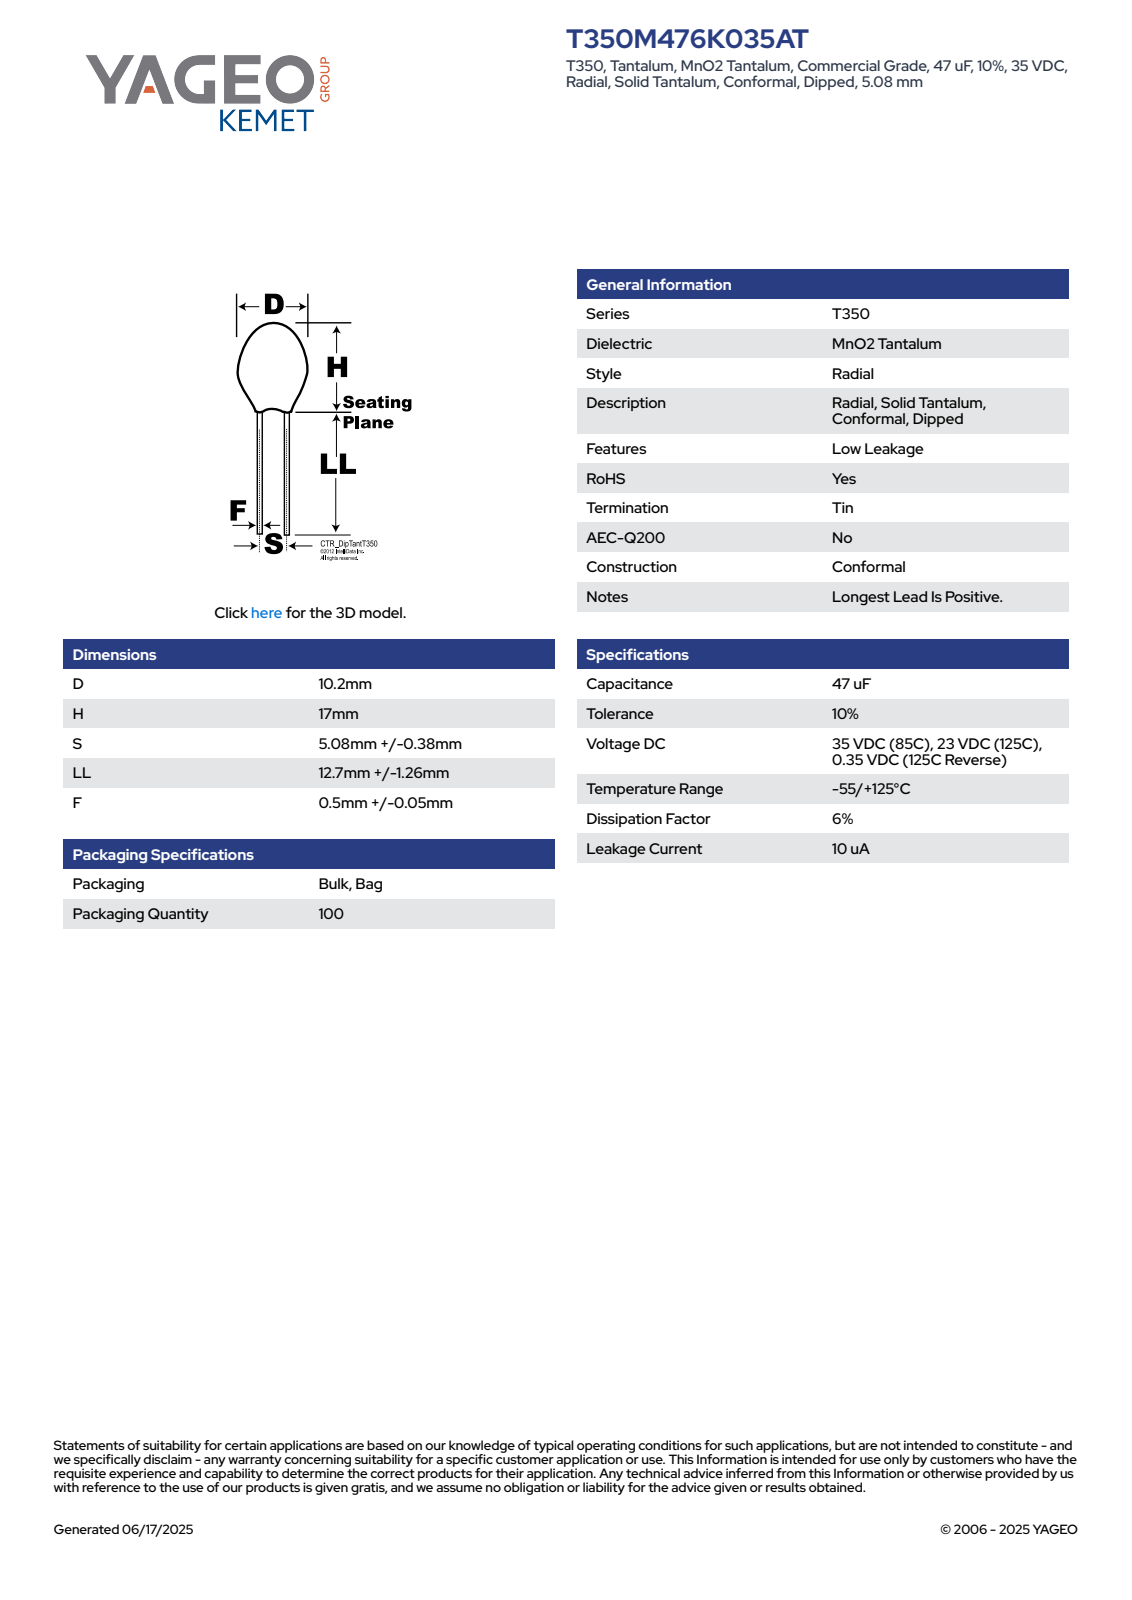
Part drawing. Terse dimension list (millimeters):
name: CTR_T350_D10.2H17S5.08LL13.96F0.55
written by: SolidWorks 2014 (AUTOMOTIVE_DESIGN)
unit: mm
bodies: 1 solid, 16 faces (4 planar, 6 cylindrical, 6 other)
size: 30.96 × 10.2 × 10.2
volume: 1 110 mm³; area: 607 mm²
bosses: 2× ⌀0.55, 1× ⌀10.2
face distances: 17, 13.96, 30.96
